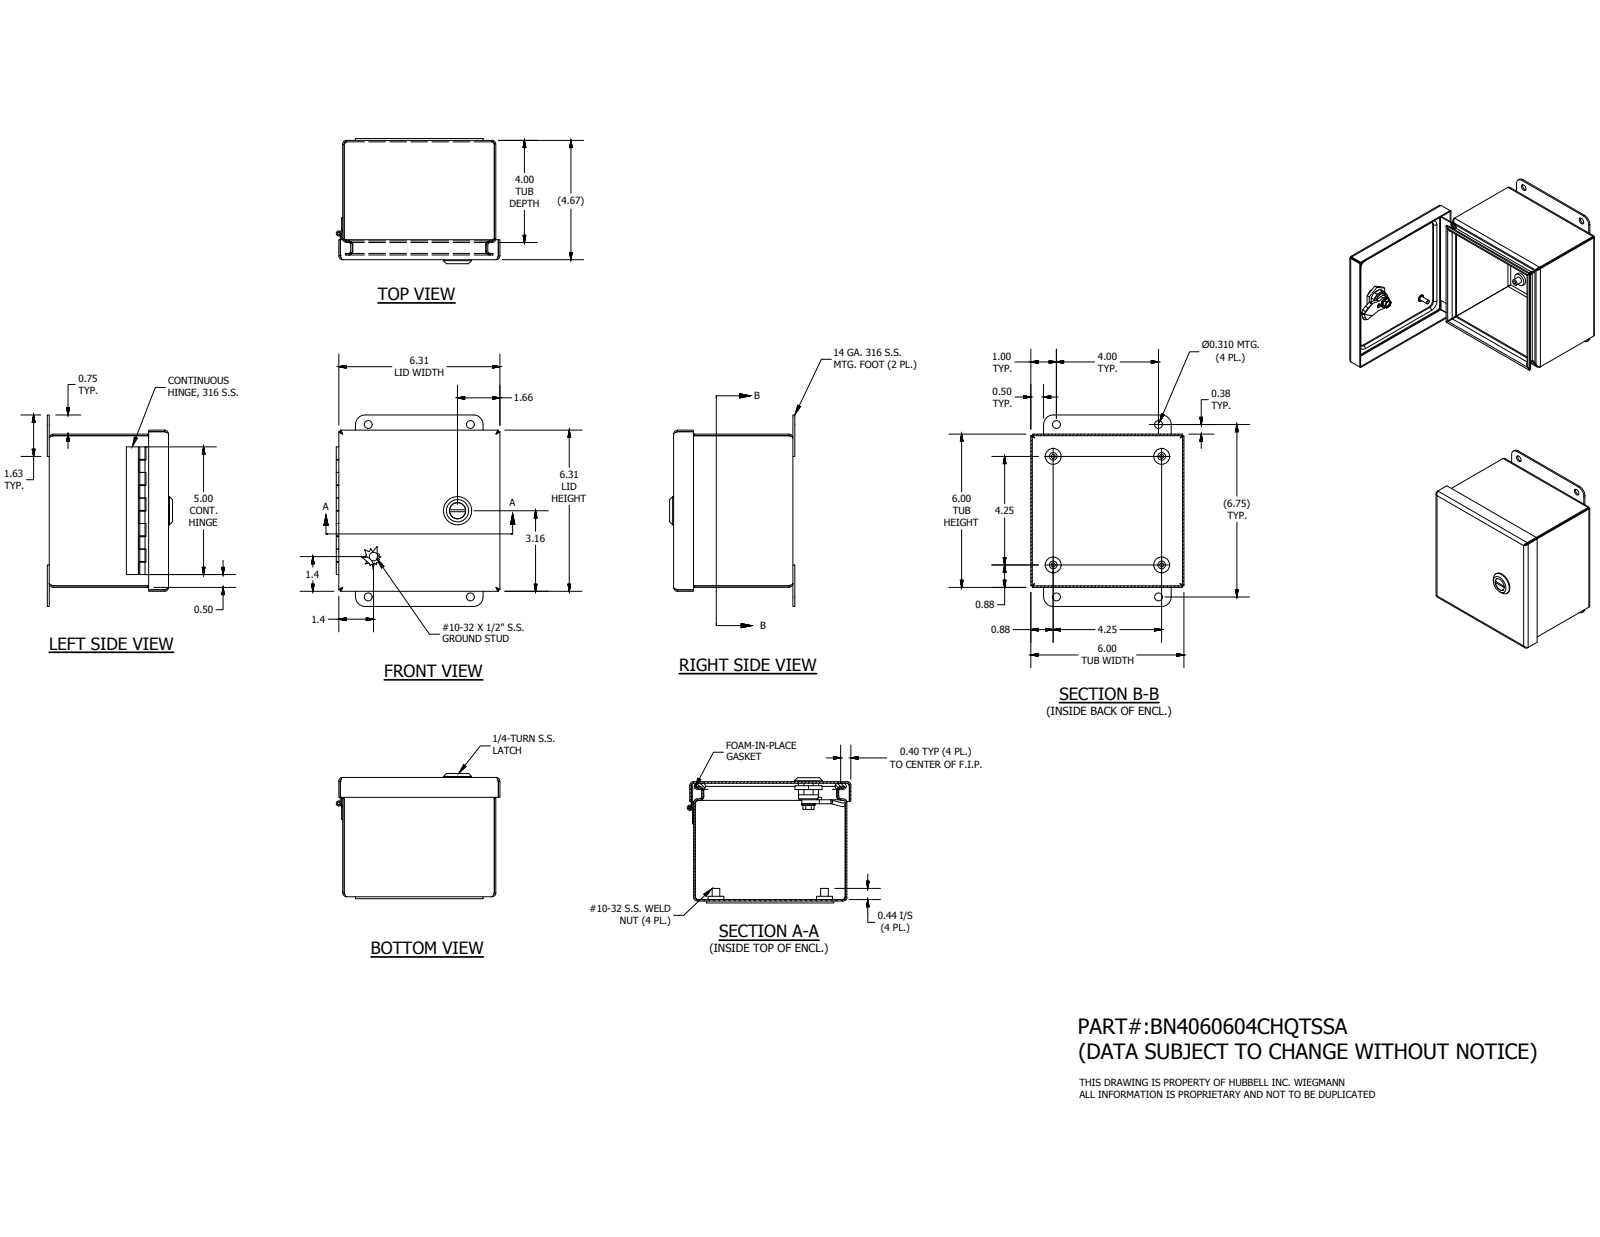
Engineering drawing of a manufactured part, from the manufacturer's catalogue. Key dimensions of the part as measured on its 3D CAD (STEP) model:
Part name (STEP PRODUCT): BN40606CHQTSSALID; 6x6; 348128; 32882LH (+8 more)
STEP written by: Autodesk Inventor 2016 (AUTOMOTIVE_DESIGN)
Units: millimetres
Bodies: 21 solids, 611 faces (330 planar, 184 cylindrical, 97 other)
Overall size (bounding box): 190.5 × 162.86 × 124.59
Volume: 270 127 mm³ · Surface area: 328 659 mm²
Round holes (diameter × count): ⌀3.96 ×4, ⌀7.87 ×4, ⌀2.96 ×1, ⌀5 ×1, ⌀8 ×1, ⌀10 ×1, ⌀10.2 ×1, ⌀16.1 ×1, ⌀20.38 ×1
Round bosses / shafts (diameter × count): ⌀15.88 ×4, ⌀7.62 ×4, ⌀28 ×1, ⌀19.8 ×1, ⌀16 ×1, ⌀15.2 ×1, ⌀13.5 ×1, ⌀12.8 ×1
Partial cylindrical surfaces — rounded edges, fillets, slot ends (radius × count): R2.38 ×20, R3.88 ×20, R3.17 ×16, R0.5 ×8, R4 ×4, R9.53 ×4, R2.31 ×2, R6.45 ×1
Main face-to-face distances: 1.5, 150.9, 1.49, 152.4, 117.19, 118.68, 115.69, 117.18, 150.91, 149.41
Hole centre spacings: 31.91, 107.95, 109.48, 139.74, 101.6, 152.66, 171.45, 174.62
